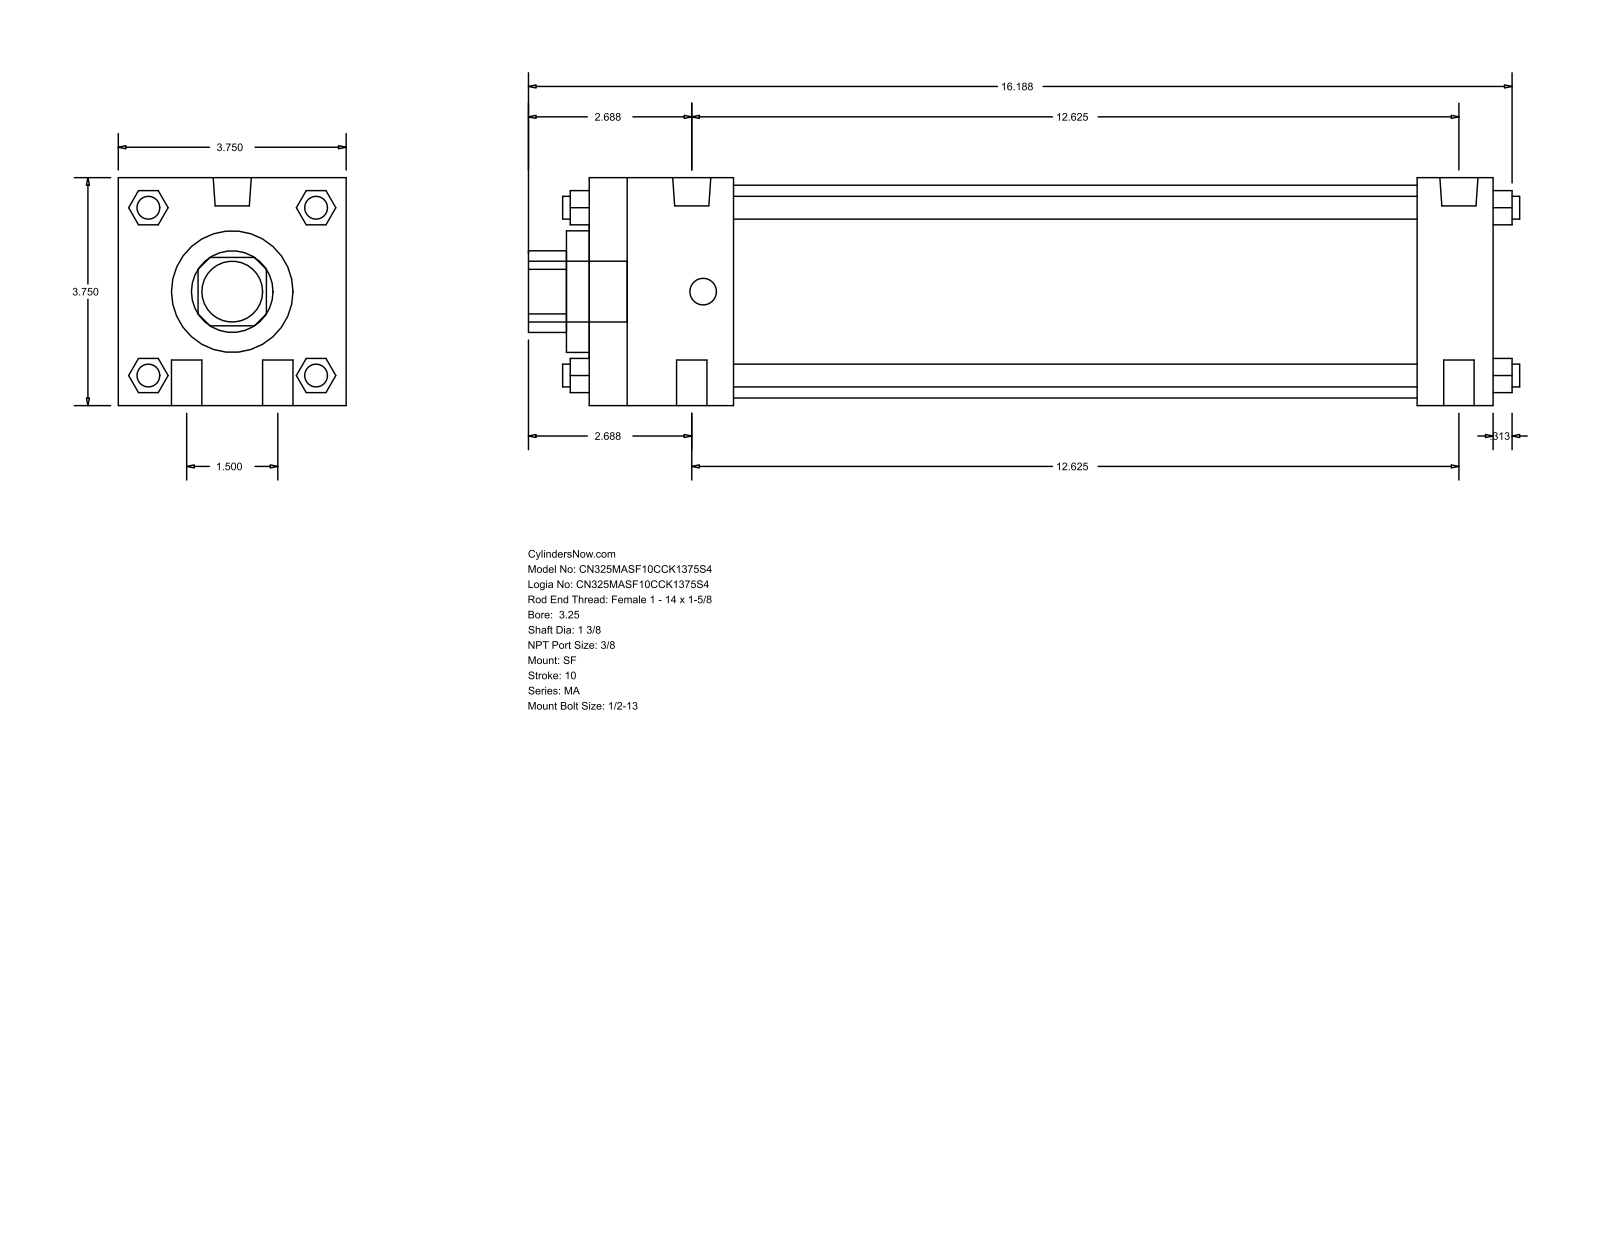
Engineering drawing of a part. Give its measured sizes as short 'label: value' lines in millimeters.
name: MA_SF__0325_1.375
written by: GSSL Pune (CONFIG_CONTROL_DESIGN)
unit: mm
bodies: 0 solids, 124 faces (94 planar, 30 cylindrical, 0 other)
size: 414.34 × 95.25 × 95.25
holes: 1× ⌀34.92, 1× ⌀50.8, 1× ⌀88.9
bosses: 4× ⌀12.7, 4× ⌀9.53, 2× ⌀15.93, 2× ⌀11.11, 1× ⌀25.4
rounds: 1× R17.06
face distances: 95.24, 377.83, 346.08, 31.75, 60.32, 285.76, 317.51, 9.52, 69.84, 355.6
